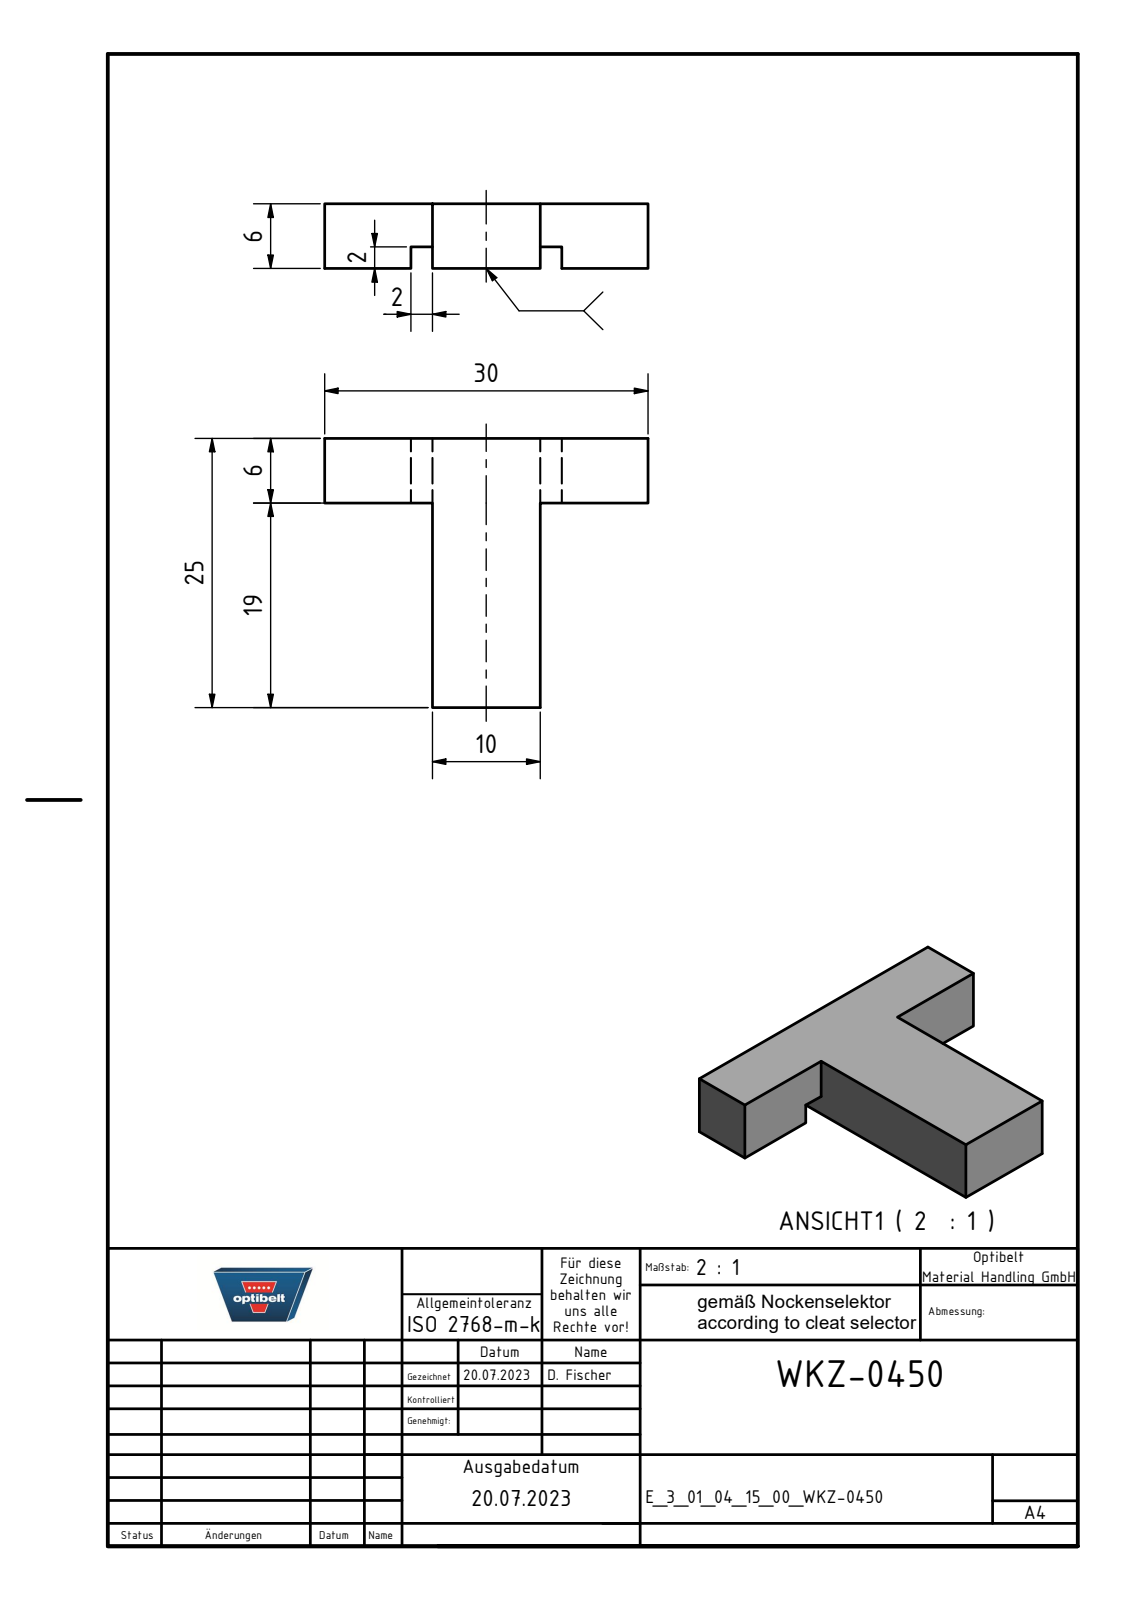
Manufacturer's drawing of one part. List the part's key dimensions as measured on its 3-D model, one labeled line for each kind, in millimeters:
Part name (STEP PRODUCT): E_3_01_04_15_00_WKZ-0450
STEP written by: Autodesk Inventor 2021 (AUTOMOTIVE_DESIGN)
Units: millimetres
Bodies: 1 solid, 16 faces (16 planar, 0 cylindrical, 0 other)
Overall size (bounding box): 30 × 25 × 6
Volume: 2 172 mm³ · Surface area: 1 432 mm²
Main face-to-face distances: 6, 10, 20, 25, 19, 2, 30, 8, 22, 12
